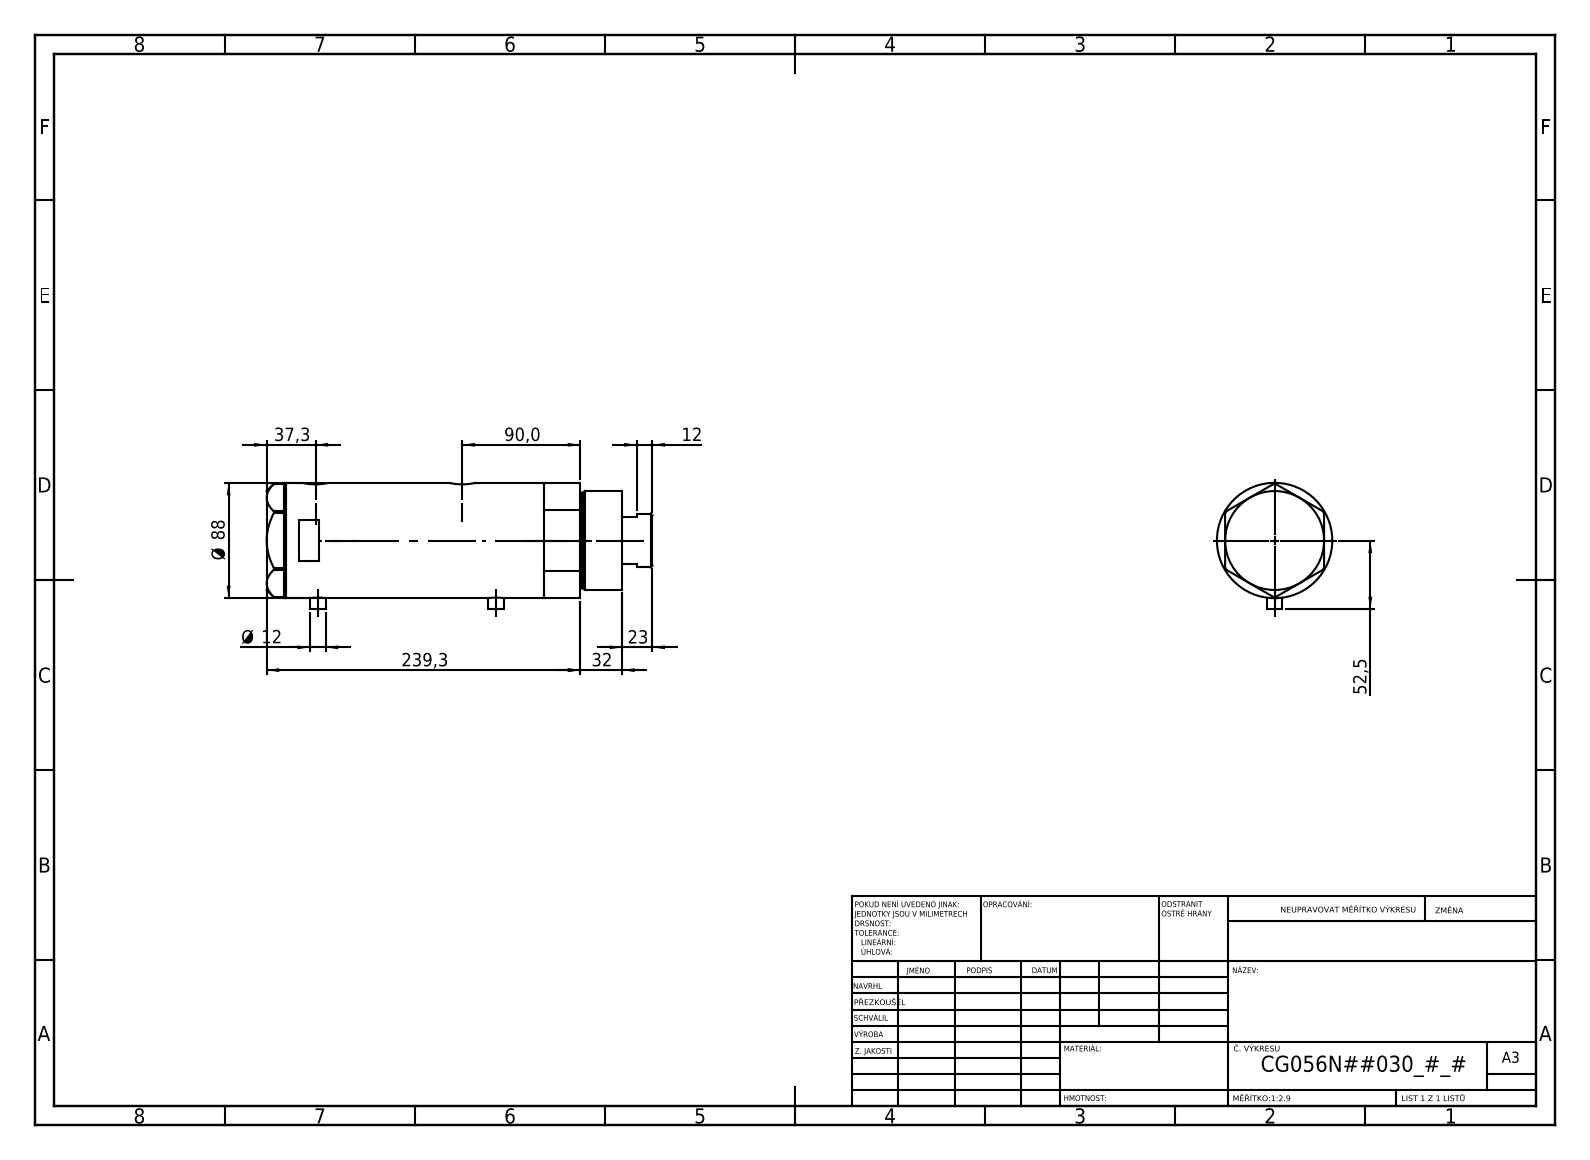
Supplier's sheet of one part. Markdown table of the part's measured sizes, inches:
| quantity | value |
| --- | --- |
| part name | V270CG_FRONT; V270CG_MIDDLE; V270CG_VC; V270CG_BACK |
| STEP written by | SolidWorks 2019 (CONFIG_CONTROL_DESIGN) |
| units | inches |
| bodies | 4 solids, 121 faces (52 planar, 49 cylindrical, 20 other) |
| overall size | 11.587 × 3.799 × 3.465 |
| volume | 94.95 in³ |
| surface area | 344.6 in² |
| round holes (diameter × count) | 0.492 × 2, 0.518 × 2, 0.787 × 2, 0.571 × 1, 1.654 × 1, 1.713 × 1, 2.205 × 1, 2.362 × 1, 3.15 × 1 |
| round bosses / shafts (diameter × count) | 0.472 × 2, 3.465 × 1, 2.953 × 1, 2.874 × 1, 1.614 × 1 |
| main face-to-face distances | 5.291, 1.024, 4.268, 0.591, 1.614, 5.882, 10.091, 10.681, 9.067, 4.799 |
| hole center spacings | 0.067, 1.016, 4.343, 4.409, 5.358, 5.425 |
